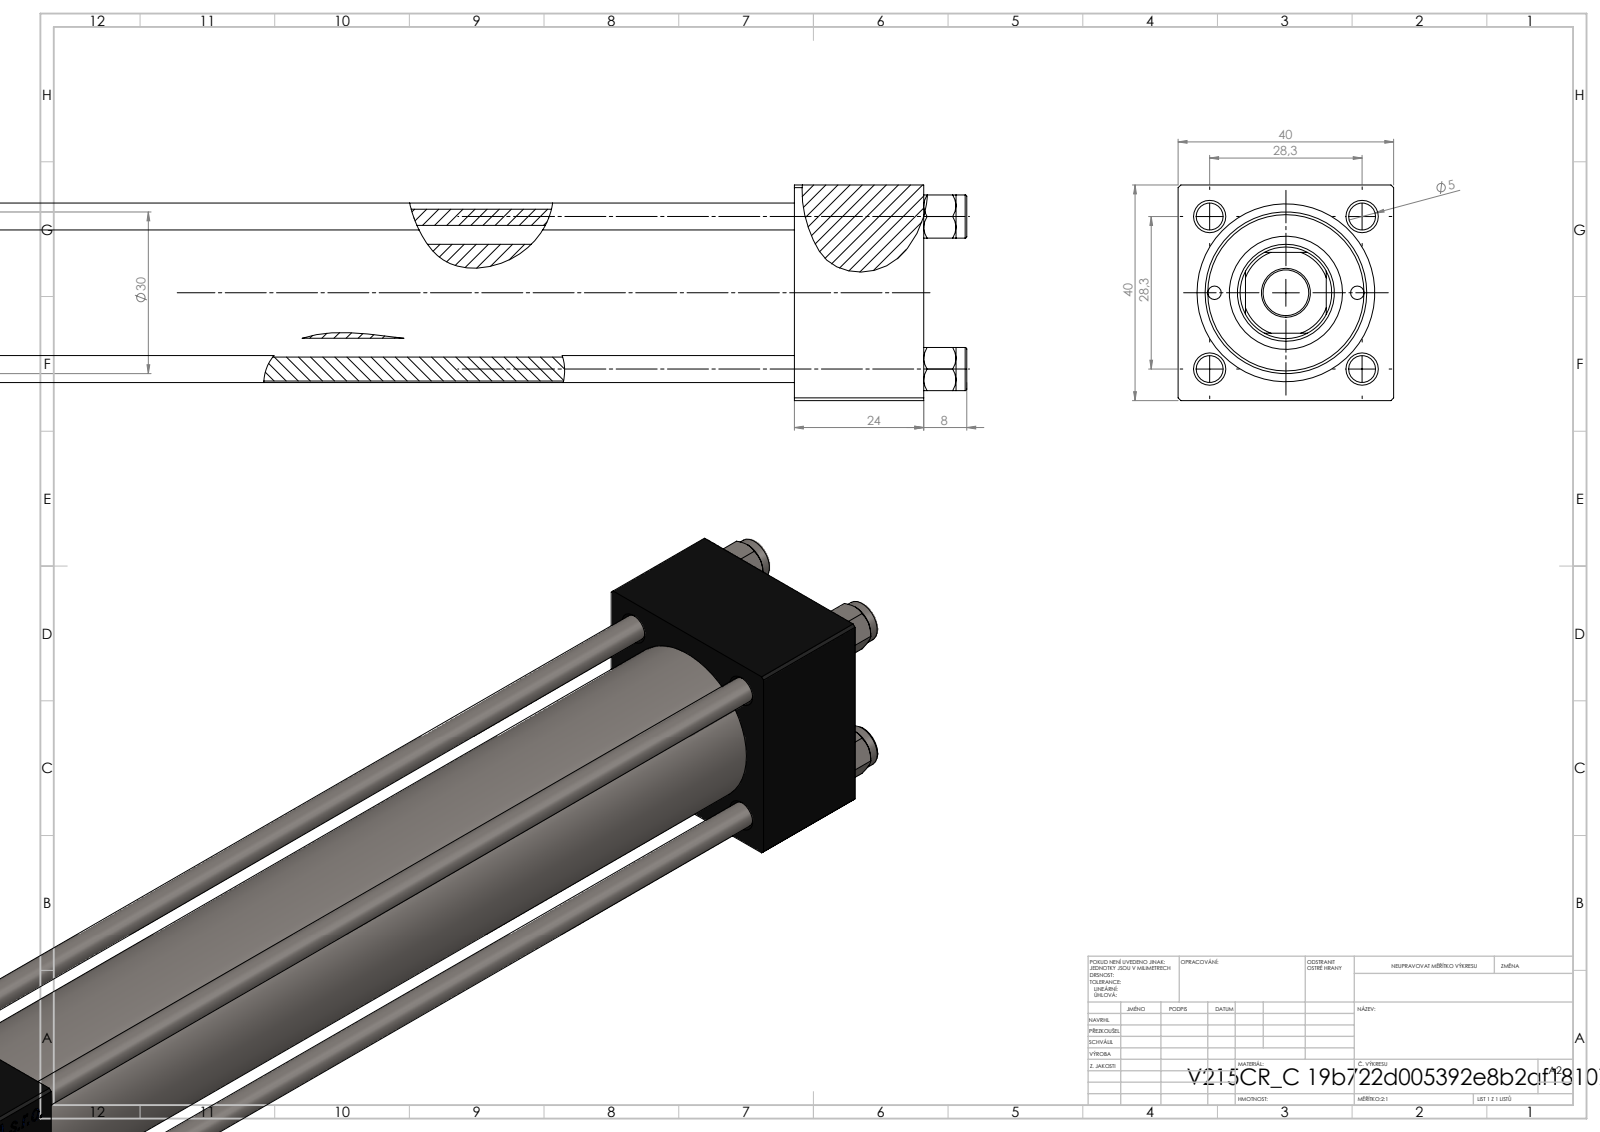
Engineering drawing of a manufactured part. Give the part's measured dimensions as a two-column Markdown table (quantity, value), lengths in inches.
| quantity | value |
| --- | --- |
| part name | V215CR_C_TYCINKA; V215_VC_A; V215CR_C_Body; V215CR_VCP_C (+1 more) |
| STEP written by | SolidWorks 2019 (CONFIG_CONTROL_DESIGN) |
| units | inches |
| bodies | 11 solids, 1150 faces (526 planar, 88 cylindrical, 536 other) |
| overall size | 11.102 × 1.575 × 1.575 |
| volume | 14.25 in³ |
| surface area | 152.3 in² |
| round holes (diameter × count) | 0.197 × 4, 0.787 × 3, 0.098 × 2, 0.276 × 2, 0.518 × 2, 0.335 × 1, 0.709 × 1, 0.827 × 1, 0.984 × 1, 1.181 × 1 |
| round bosses / shafts (diameter × count) | 0.315 × 4, 1.22 × 1 |
| partial cylindrical surfaces (radius × count) | 0.335 × 1 |
| main face-to-face distances | 1.575, 0.945, 8.307, 7.362, 9.067, 8.122, 0.76, 1.89, 10.197, 9.252 |
| hole center spacings | 0.558, 0.788, 1.114, 1.214, 0.522, 1.576, 1.043, 8.346 |
